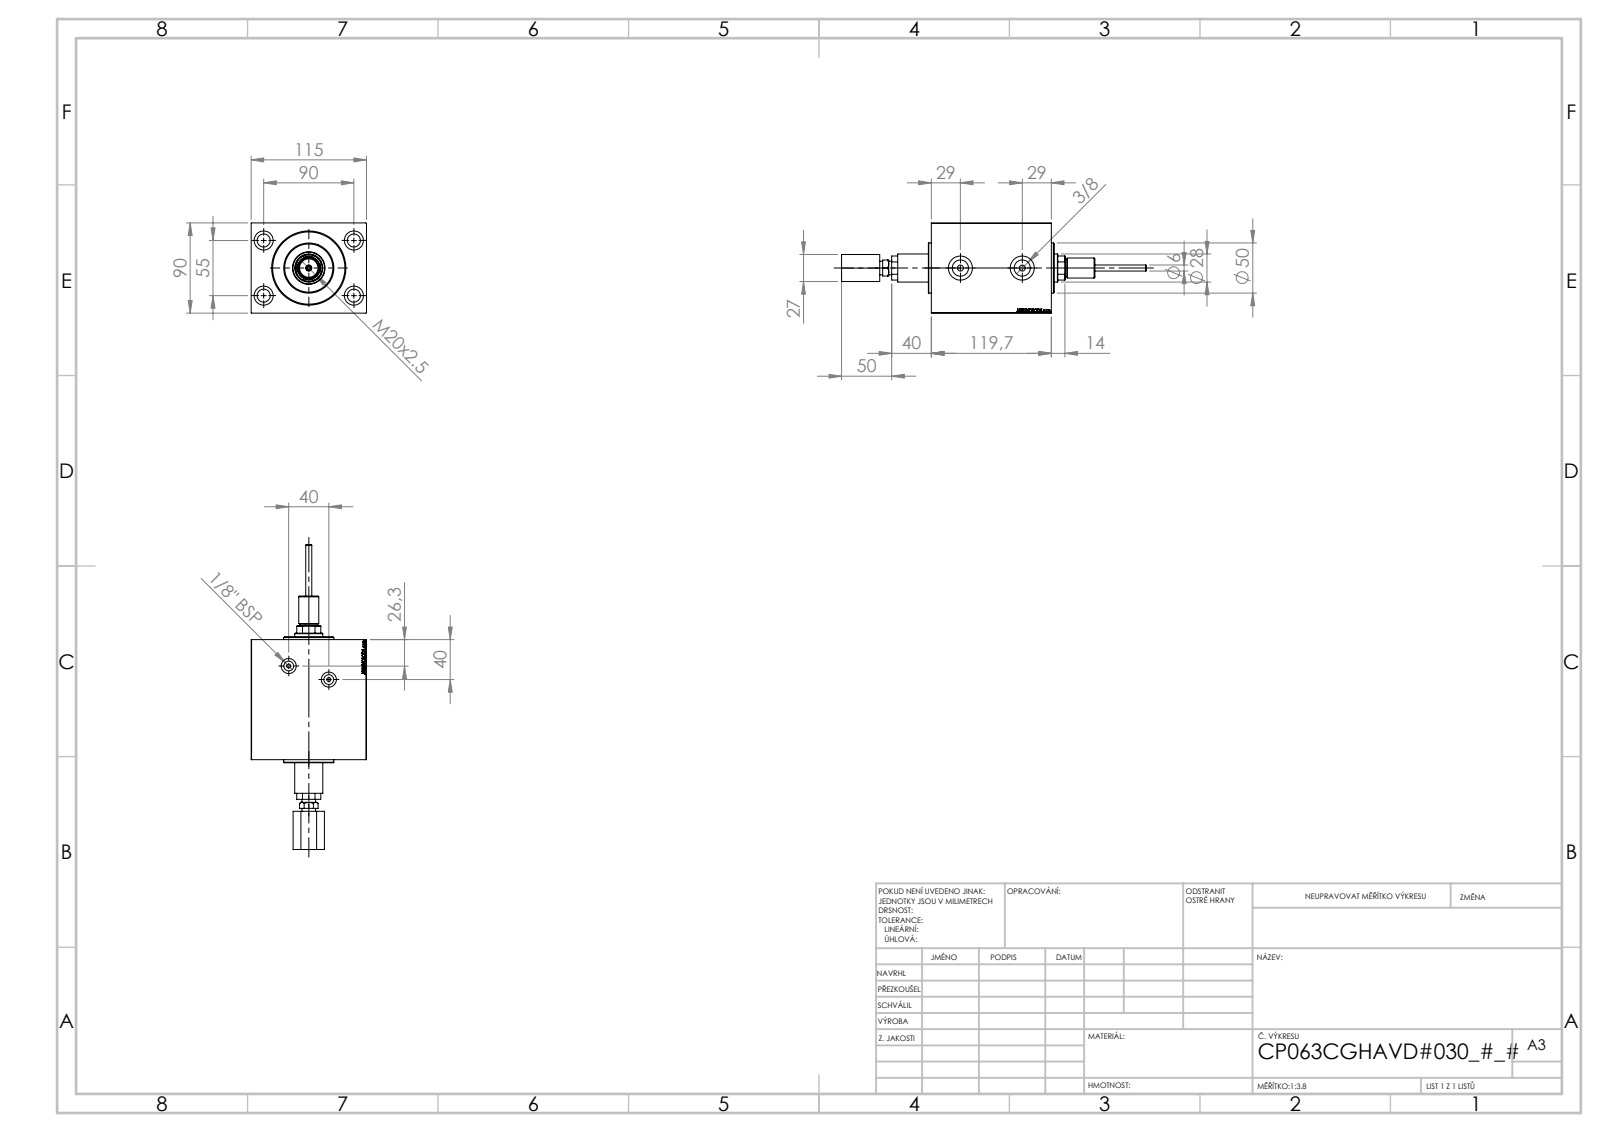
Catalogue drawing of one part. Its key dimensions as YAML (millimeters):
part_name: "V450DCP_B_RodCooling_ACCESSORIES; V450DCP_B_VCP; V450CP_MALE_METRIC; V450DCP_VC_B (+1 more)"
step_written_by: "SolidWorks 2019 (CONFIG_CONTROL_DESIGN)"
units: millimeters
bodies: {solids: 5, faces: 970, planar: 446, cylindrical: 106, other: 418}
overall_size: [303.7, 115, 90]
volume: 1143000
surface_area: 176423
round_holes:
  - {diameter: 13, count: 4}
  - {diameter: 19, count: 4}
  - {diameter: 6, count: 3}
  - {diameter: 4, count: 2}
  - {diameter: 9.73, count: 2}
  - {diameter: 15, count: 2}
  - {diameter: 16.17, count: 2}
  - {diameter: 24, count: 2}
  - {diameter: 3, count: 1}
  - {diameter: 18.5, count: 1}
  - {diameter: 28, count: 1}
  - {diameter: 31.5, count: 1}
round_bosses_or_shafts:
  - {diameter: 50, count: 1}
  - {diameter: 20, count: 1}
  - {diameter: 18, count: 1}
  - {diameter: 13.47, count: 1}
partial_cylinders:
  - {radius: 13.5, count: 1}
face_to_face_distances: [90, 115, 102.2, 30, 119.7, 17.5, 1, 118.7, 16.5, 42.2]
hole_center_spacings: [52.74, 55, 90, 105.48, 42.22, 61.7]
